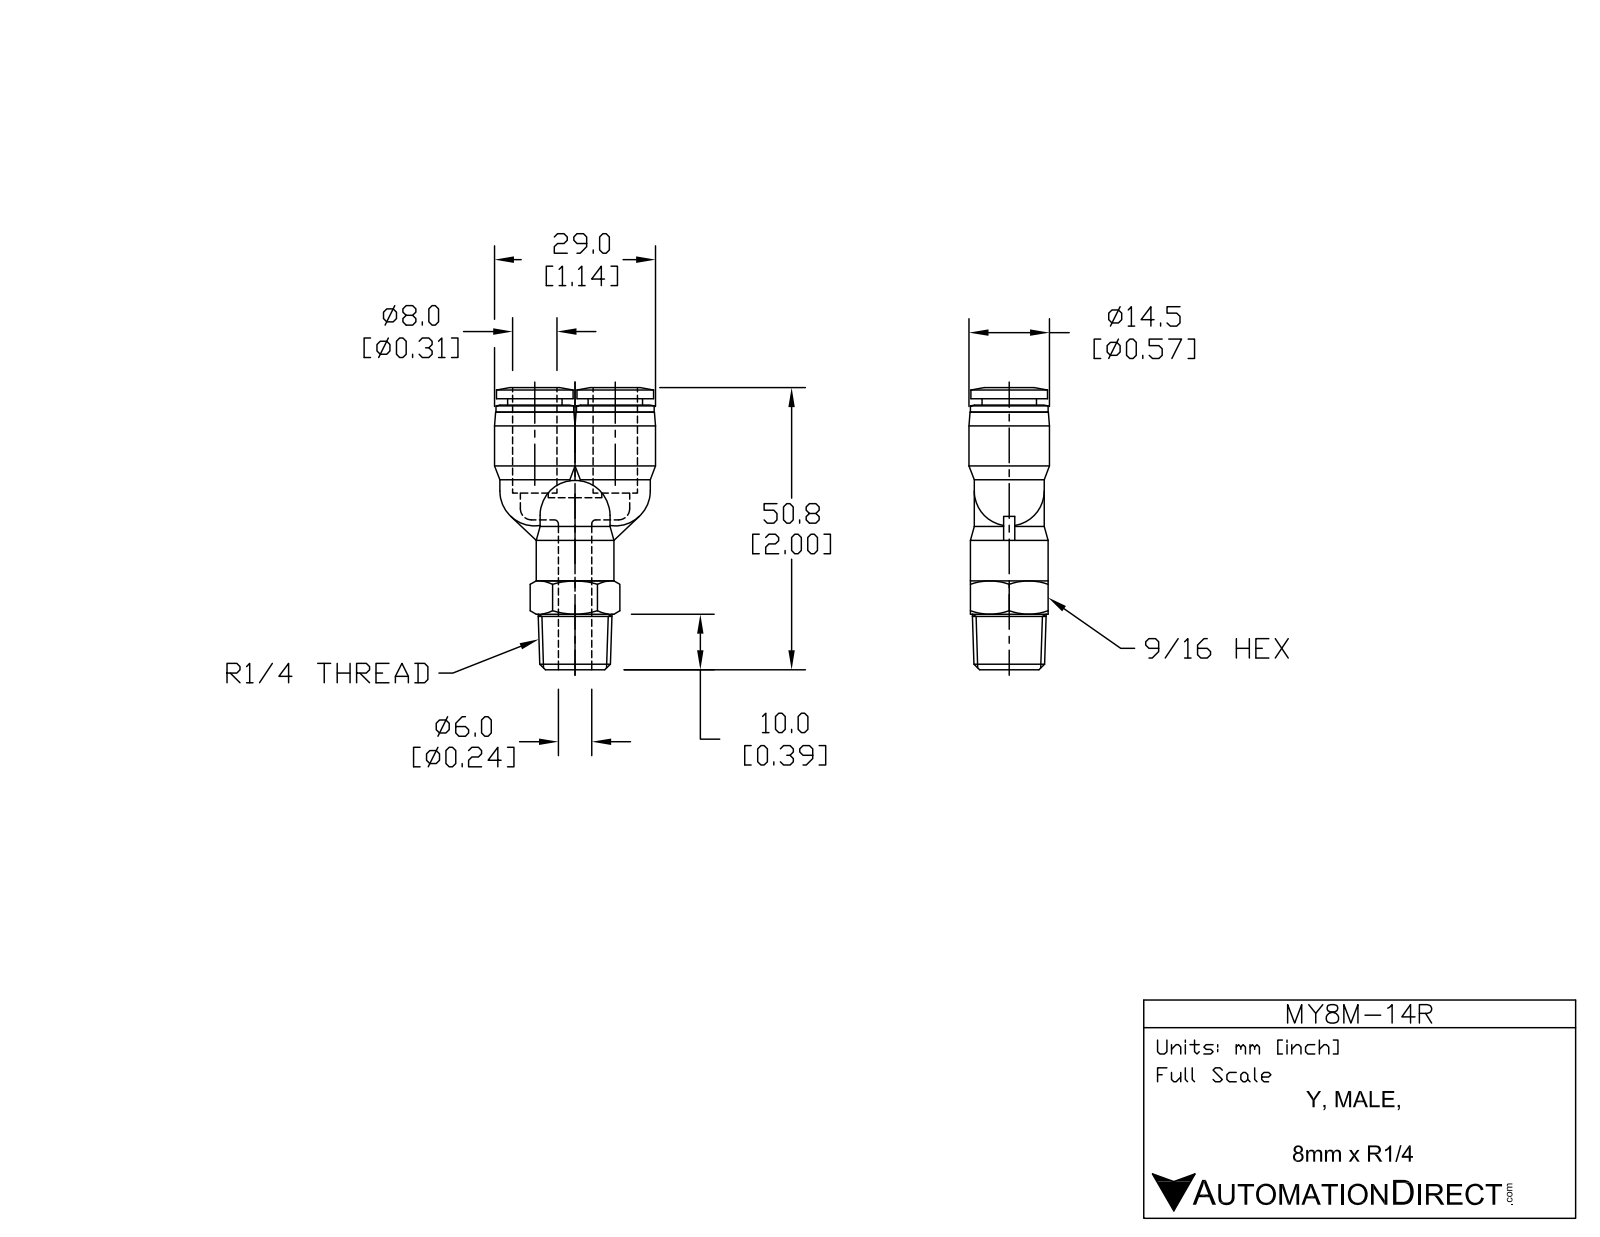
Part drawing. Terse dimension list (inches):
name: MY8M-14R
written by: SolidWorks 2015 (AUTOMOTIVE_DESIGN)
unit: in
bodies: 1 solid, 105 faces (23 planar, 35 cylindrical, 47 other)
size: 1.984 × 1.142 × 0.571
volume: 0.462 in³; area: 8.622 in²
holes: 4× ⌀0.236, 2× ⌀0.327
bosses: 3× ⌀0.551, 3× ⌀0.496, 2× ⌀0.571, 2× ⌀0.543, 2× ⌀0.386
face distances: 0.551, 0.045, 1.86, 1.906, 1.252, 0.608, 0.654, 0.079, 0.236, 0.315
hole spacings: 0.285, 0.571
